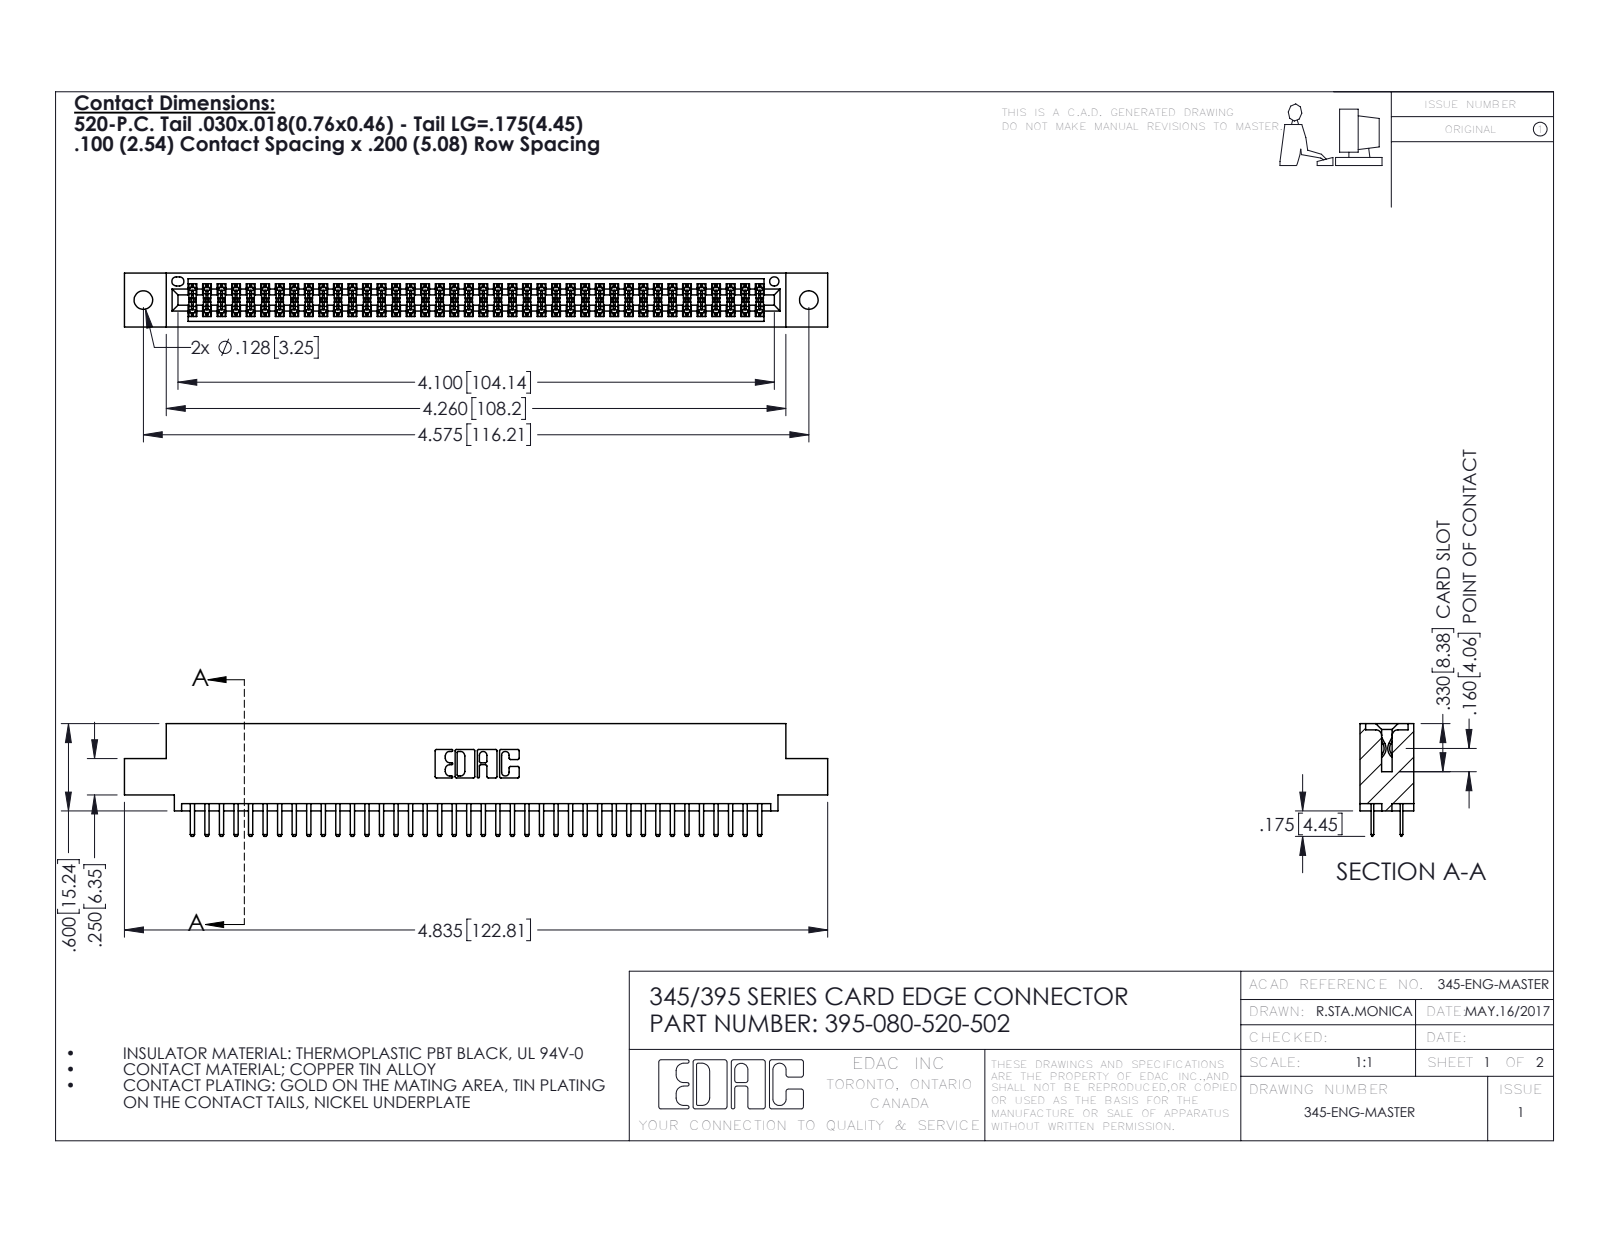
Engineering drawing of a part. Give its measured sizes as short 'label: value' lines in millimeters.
name: 345-292-001_345-293-120; 395-080-520-502; 345 Part_0.110 Offset - 0.128 Dia
written by: SolidWorks 2016 (CONFIG_CONTROL_DESIGN)
unit: mm
bodies: 81 solids, 4450 faces (2884 planar, 1566 cylindrical, 0 other)
size: 122.8 × 19.7 × 9.4
volume: 11 800 mm³; area: 17 100 mm²
holes: 2× ⌀3.3, 1× ⌀1.6
rounds: 120× R0.2, 84× R0.3, 22× R0.3, 6× R0.2, 6× R0.8, 3× R0.7, 2× R0.4, 2× R0.5
face distances: 7.6, 1.8, 5.1, 9.4, 2.5, 6.9, 0.6, 5.7, 0.6, 1.8
hole spacings: 6.9, 110.2, 116.2
